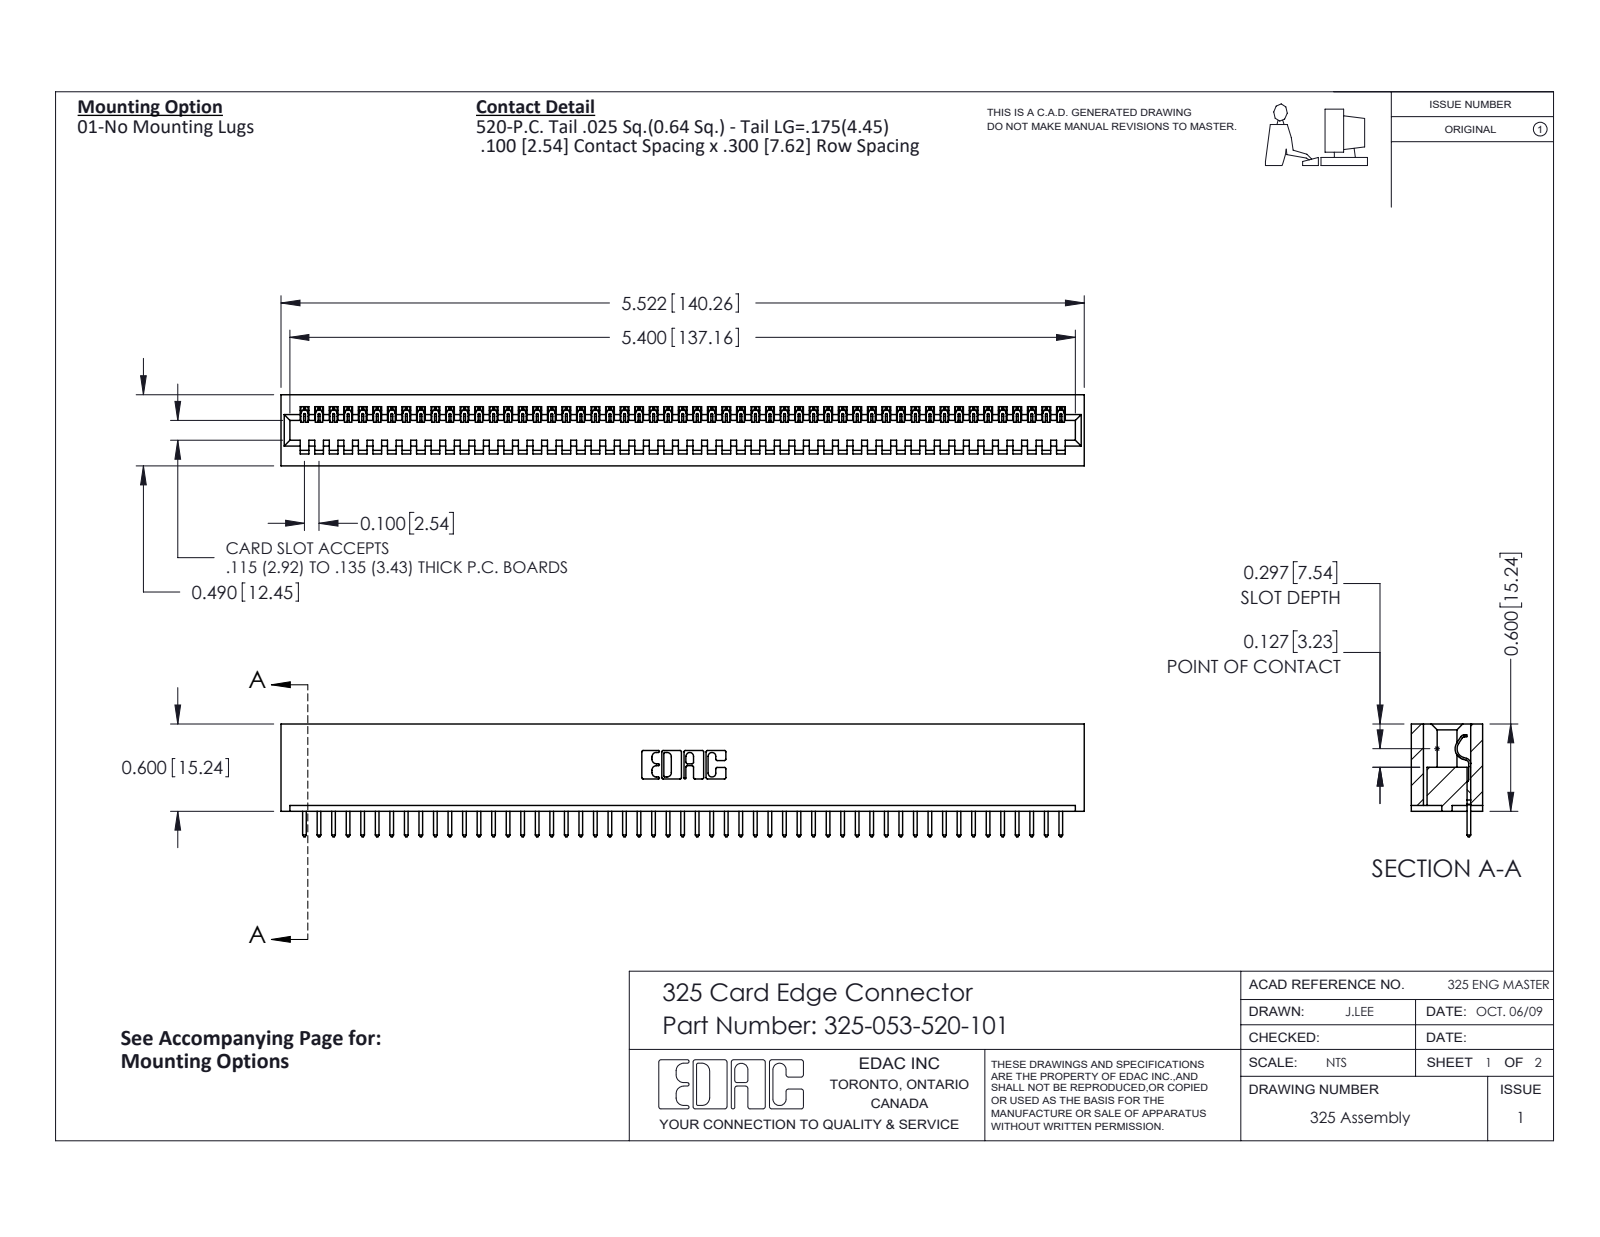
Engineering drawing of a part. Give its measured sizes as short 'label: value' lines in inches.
name: 325 Part_Lugless; 325-053-520-101; 325-292-001_325-293-120
written by: SolidWorks 2016 (CONFIG_CONTROL_DESIGN)
unit: in
bodies: 54 solids, 3180 faces (2292 planar, 888 cylindrical, 0 other)
size: 5.522 × 0.775 × 0.49
volume: 1.118 in³; area: 31.22 in²
rounds: 106× R0.006, 106× R0.01, 22× R0.01, 6× R0.007, 6× R0.031, 3× R0.026, 1× R0.014, 1× R0.022
face distances: 0.083, 0.407, 0.49, 0.3, 0.107, 0.383, 0.025, 0.325, 0.263, 0.56
